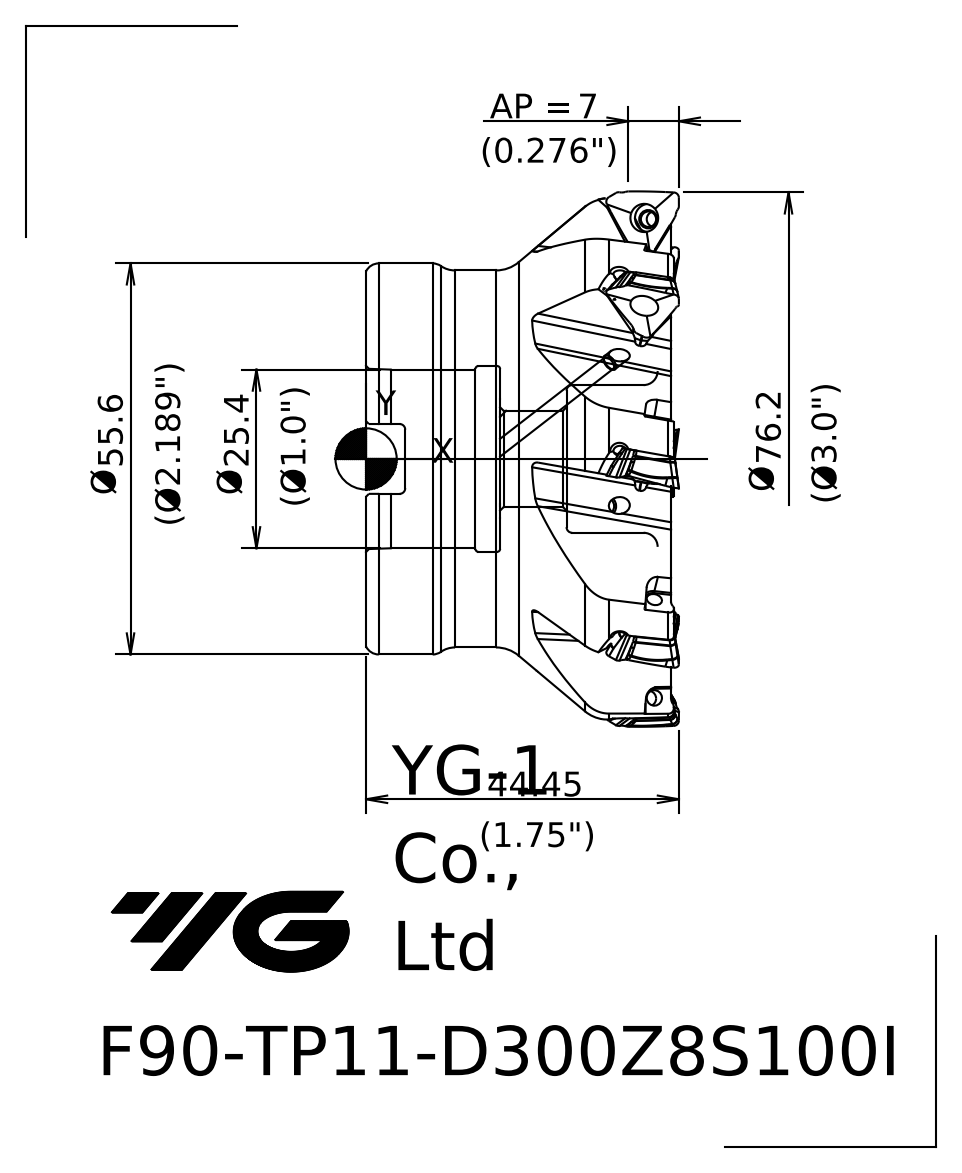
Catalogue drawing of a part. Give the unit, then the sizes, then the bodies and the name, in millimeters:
Units: millimetres
Overall size (bounding box): 76.25 × 76.25 × 44.45
Round holes (diameter × count): ⌀13.7 ×1, ⌀21 ×1, ⌀25.4 ×1, ⌀26.4 ×1
Round bosses / shafts (diameter × count): ⌀55.6 ×1, ⌀53.6 ×1
Partial cylindrical surfaces — rounded edges, fillets, slot ends (radius × count): R0.8 ×2
Main face-to-face distances: 43.35, 1.9, 41.45, 24.3, 22.4, 19.05, 37.79, 35.89, 13.49, 5.56
Volume: 112 924 mm³ · Surface area: 25 191 mm²
Bodies: 1 solid, 76 faces (18 planar, 10 cylindrical, 48 other)
Part name (STEP PRODUCT): 1022B364674Envod
STEP written by: SIEMENS PLM Software NX 10.0 (AP203_CONFIGURATION_CONTROLLED_3D_DESIGN_OF_MECHANICAL_PARTS_AND_ASSEMBLIES_MIM_LF)
